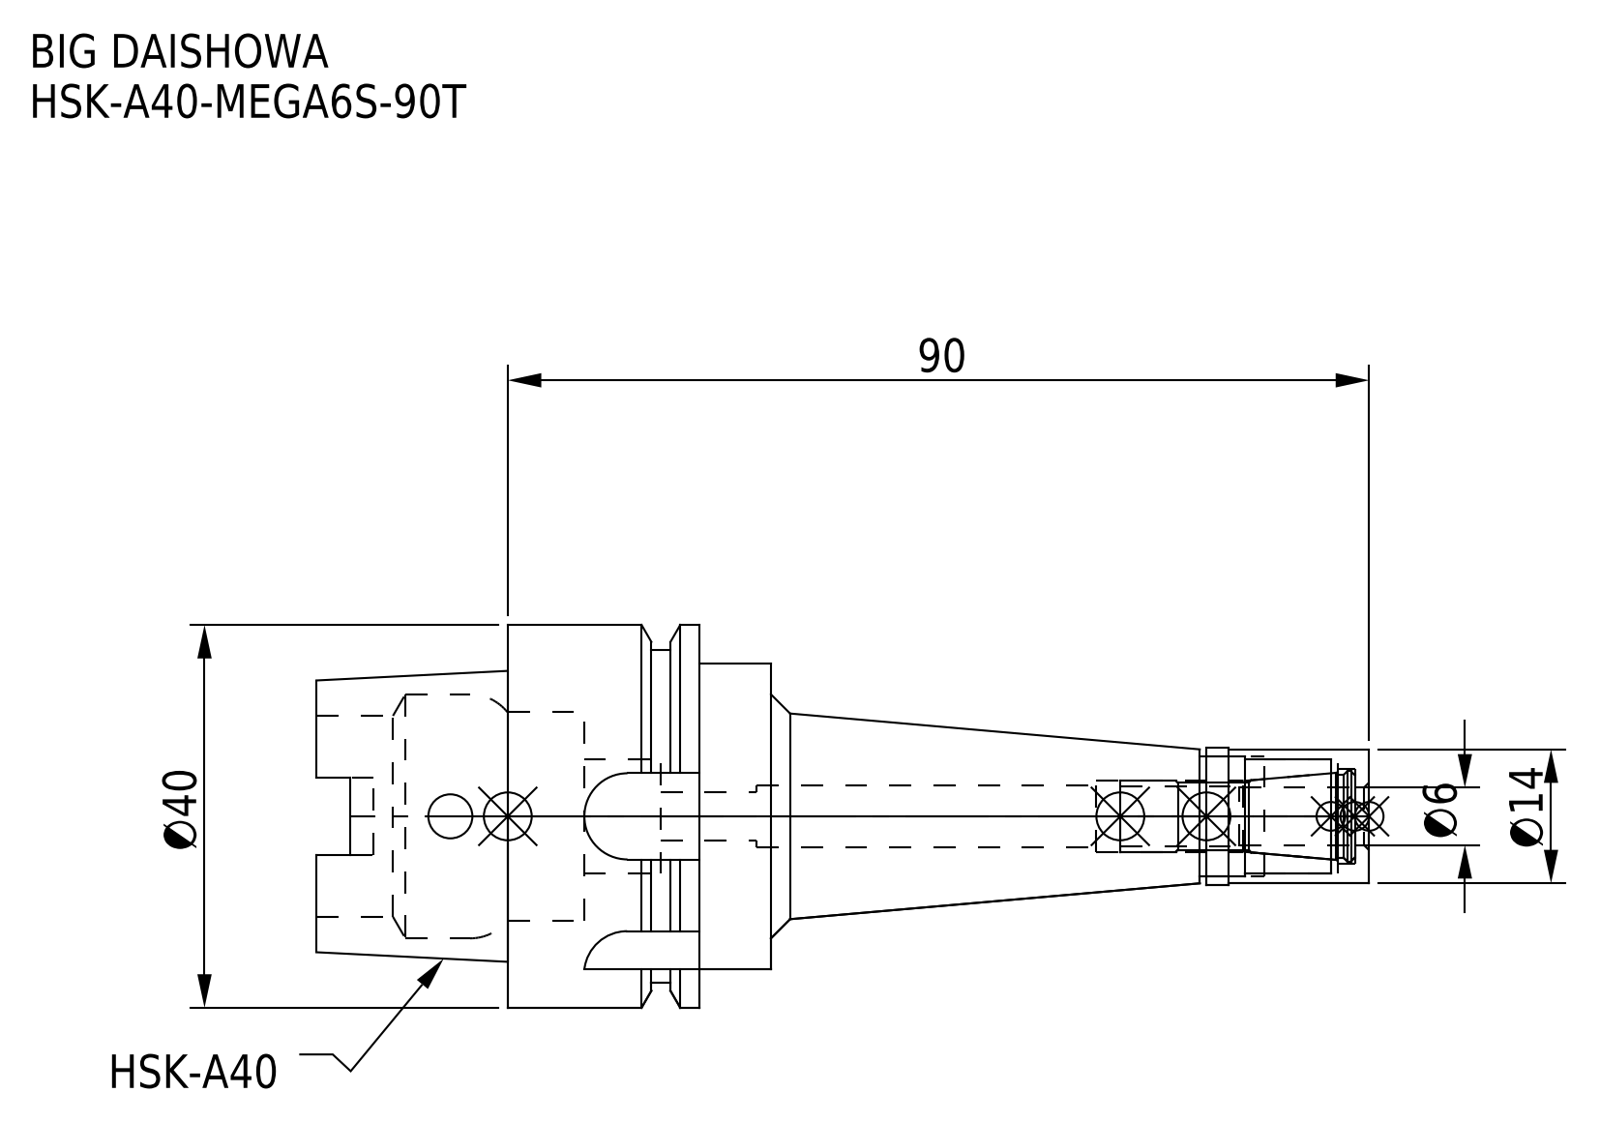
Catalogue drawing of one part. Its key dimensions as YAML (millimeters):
part_name: "MGN6S_1.stp; HSK-A40-MEGA6S-90T-060-FreeParts; HSK-A40-MEGA6S-90T-060.stp; HA40MS06090T-060_ASM.stp (+3 more)"
step_written_by: "SolidWorks 2019 (CONFIG_CONTROL_DESIGN)"
units: millimeters
bodies: {solids: 2, faces: 123, planar: 47, cylindrical: 54, other: 22}
overall_size: [110, 40, 40]
volume: 42018
surface_area: 16060
round_holes:
  - {diameter: 4.6, count: 1}
  - {diameter: 5, count: 1}
  - {diameter: 6.1, count: 1}
  - {diameter: 6.4, count: 1}
  - {diameter: 7.4, count: 1}
  - {diameter: 10, count: 1}
  - {diameter: 12, count: 1}
  - {diameter: 12.5, count: 1}
  - {diameter: 21, count: 1}
  - {diameter: 21.8, count: 1}
  - {diameter: 25.5, count: 1}
round_bosses_or_shafts:
  - {diameter: 40, count: 1}
  - {diameter: 34.8, count: 1}
  - {diameter: 32, count: 1}
  - {diameter: 14.3, count: 1}
  - {diameter: 14, count: 1}
partial_cylinders:
  - {radius: 1.88, count: 4}
  - {radius: 4.5, count: 4}
face_to_face_distances: [20, 7.5, 27.5, 19.55, 12.05, 7.95, 40, 47.5, 27.95, 34]
